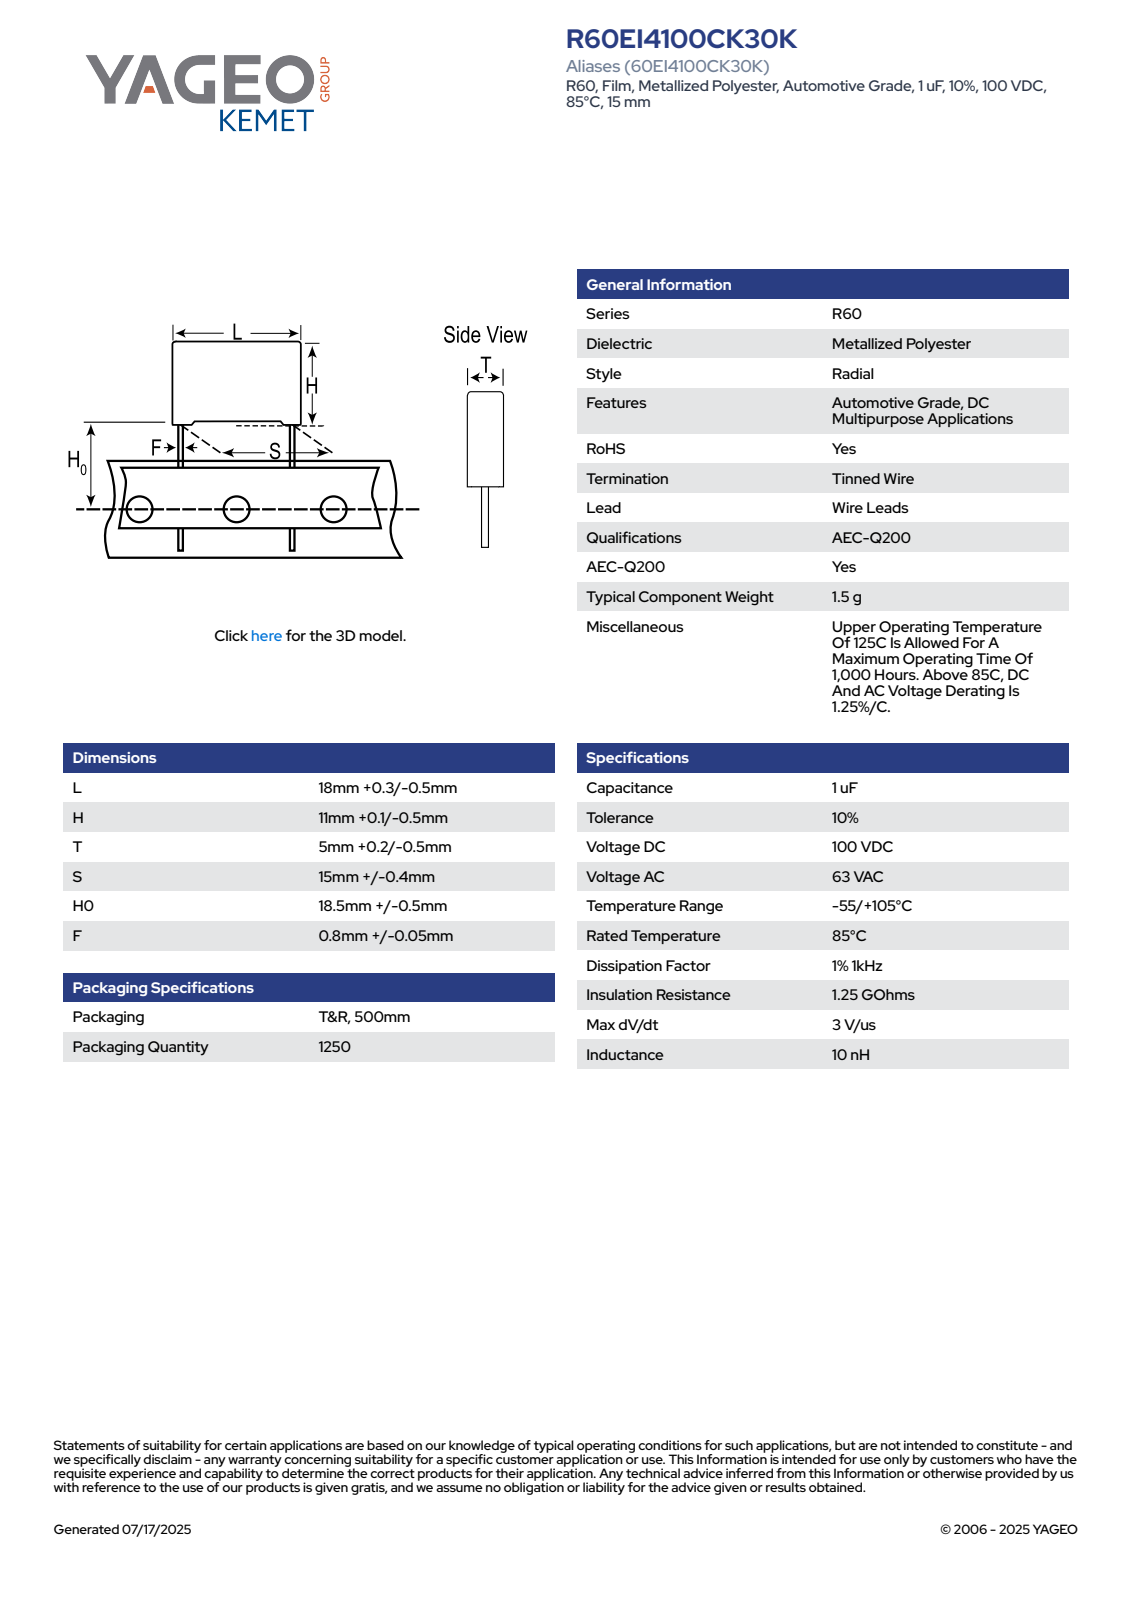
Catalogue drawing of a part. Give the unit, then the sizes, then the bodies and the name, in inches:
Units: inches
Overall size (bounding box): 1.185 × 0.72 × 0.205
Round bosses / shafts (diameter × count): ⌀0.033 ×2
Partial cylindrical surfaces — rounded edges, fillets, slot ends (radius × count): R0.02 ×4
Main face-to-face distances: 0.205, 0.407, 0.72, 0.024, 0.181, 0.015, 0.422, 0.015, 0.03, 0.437
Volume: 0.062 in³ · Surface area: 1.31 in²
Bodies: 4 solids, 85 faces (77 planar, 8 cylindrical, 0 other)
Part name (STEP PRODUCT): CFR_RB2_18X11X5_L18.3H11.1T5.2S15H019F0.85
STEP written by: SolidWorks 2021 (AUTOMOTIVE_DESIGN)
